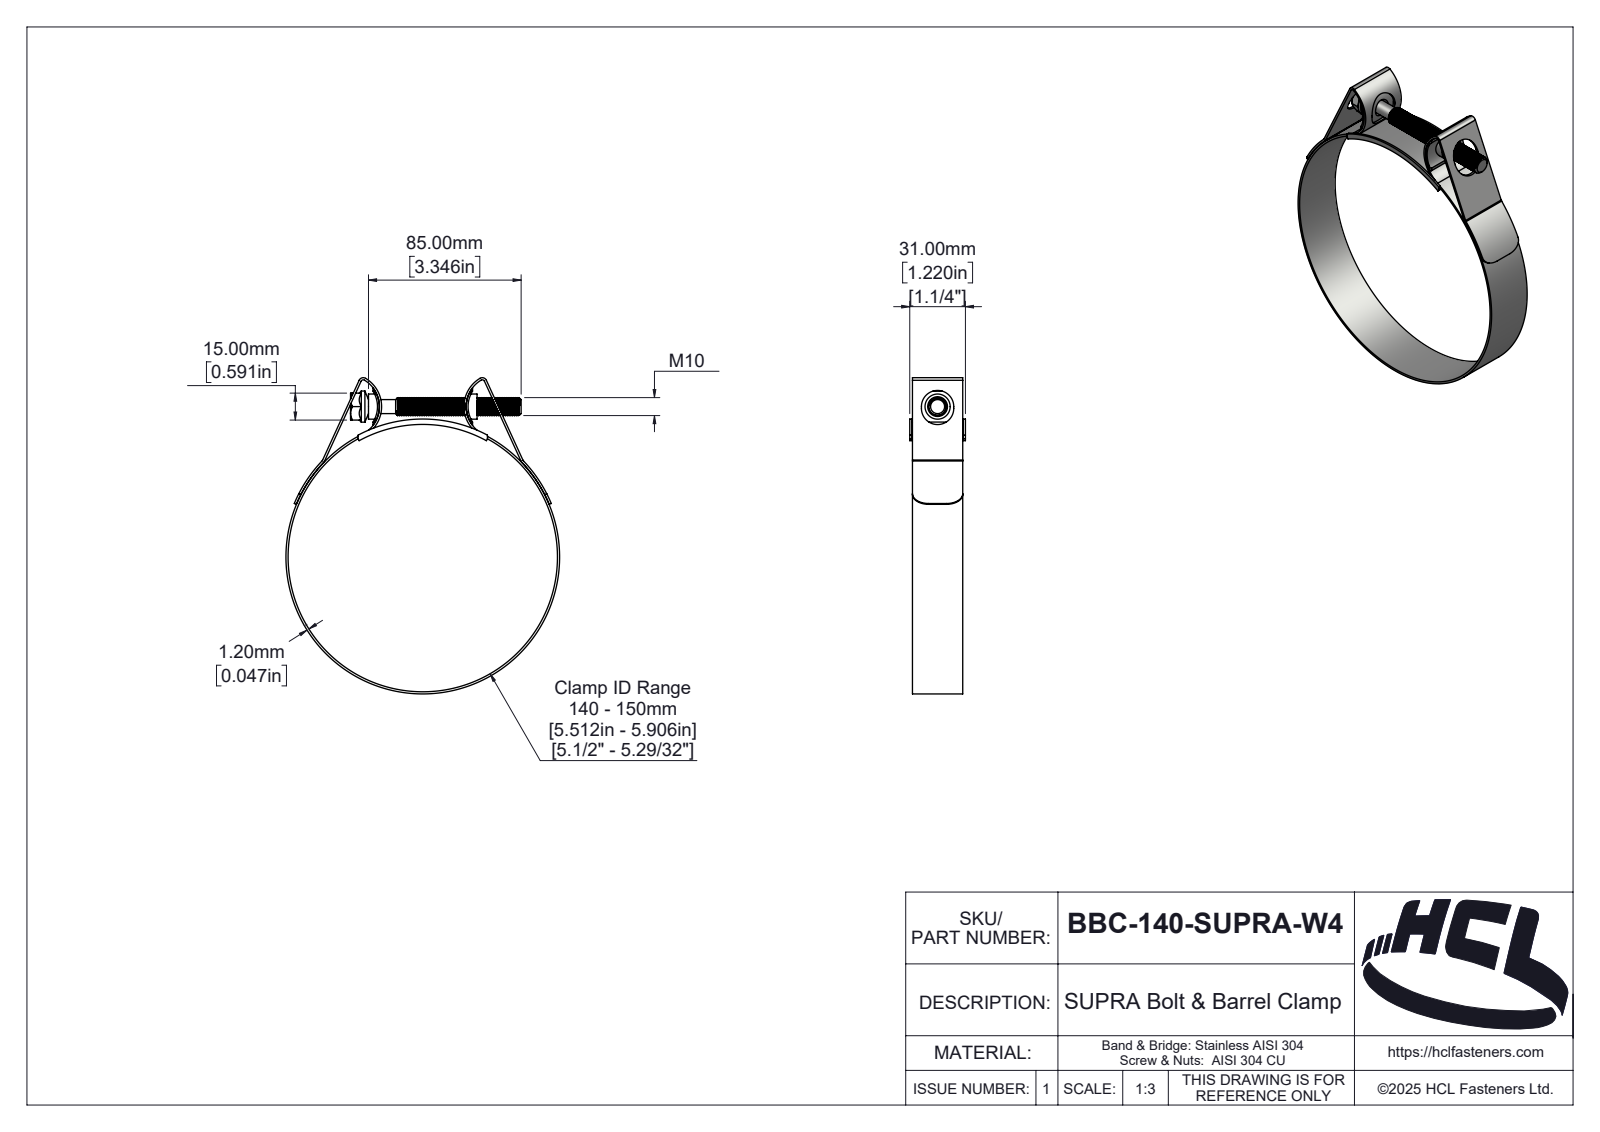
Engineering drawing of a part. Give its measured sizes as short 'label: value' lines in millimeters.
name: BBC-140-SUPRA-W4
written by: SolidWorks 2025 (AUTOMOTIVE_DESIGN)
unit: mm
bodies: 5 solids, 380 faces (46 planar, 248 cylindrical, 86 other)
size: 176.02 × 152.4 × 31
volume: 32 481 mm³; area: 48 473 mm²
holes: 1× ⌀150
bosses: 1× ⌀152.4, 1× ⌀17.32, 1× ⌀14, 1× ⌀10, 1× ⌀7.8
rounds: 4× R1, 2× R1.3, 2× R2, 2× R2.5, 2× R3.2, 2× R9, 2× R16.03, 2× R17.03
face distances: 1.2, 28, 1.5, 29.5, 29.8, 28.3, 31, 28.6, 15, 2.5
